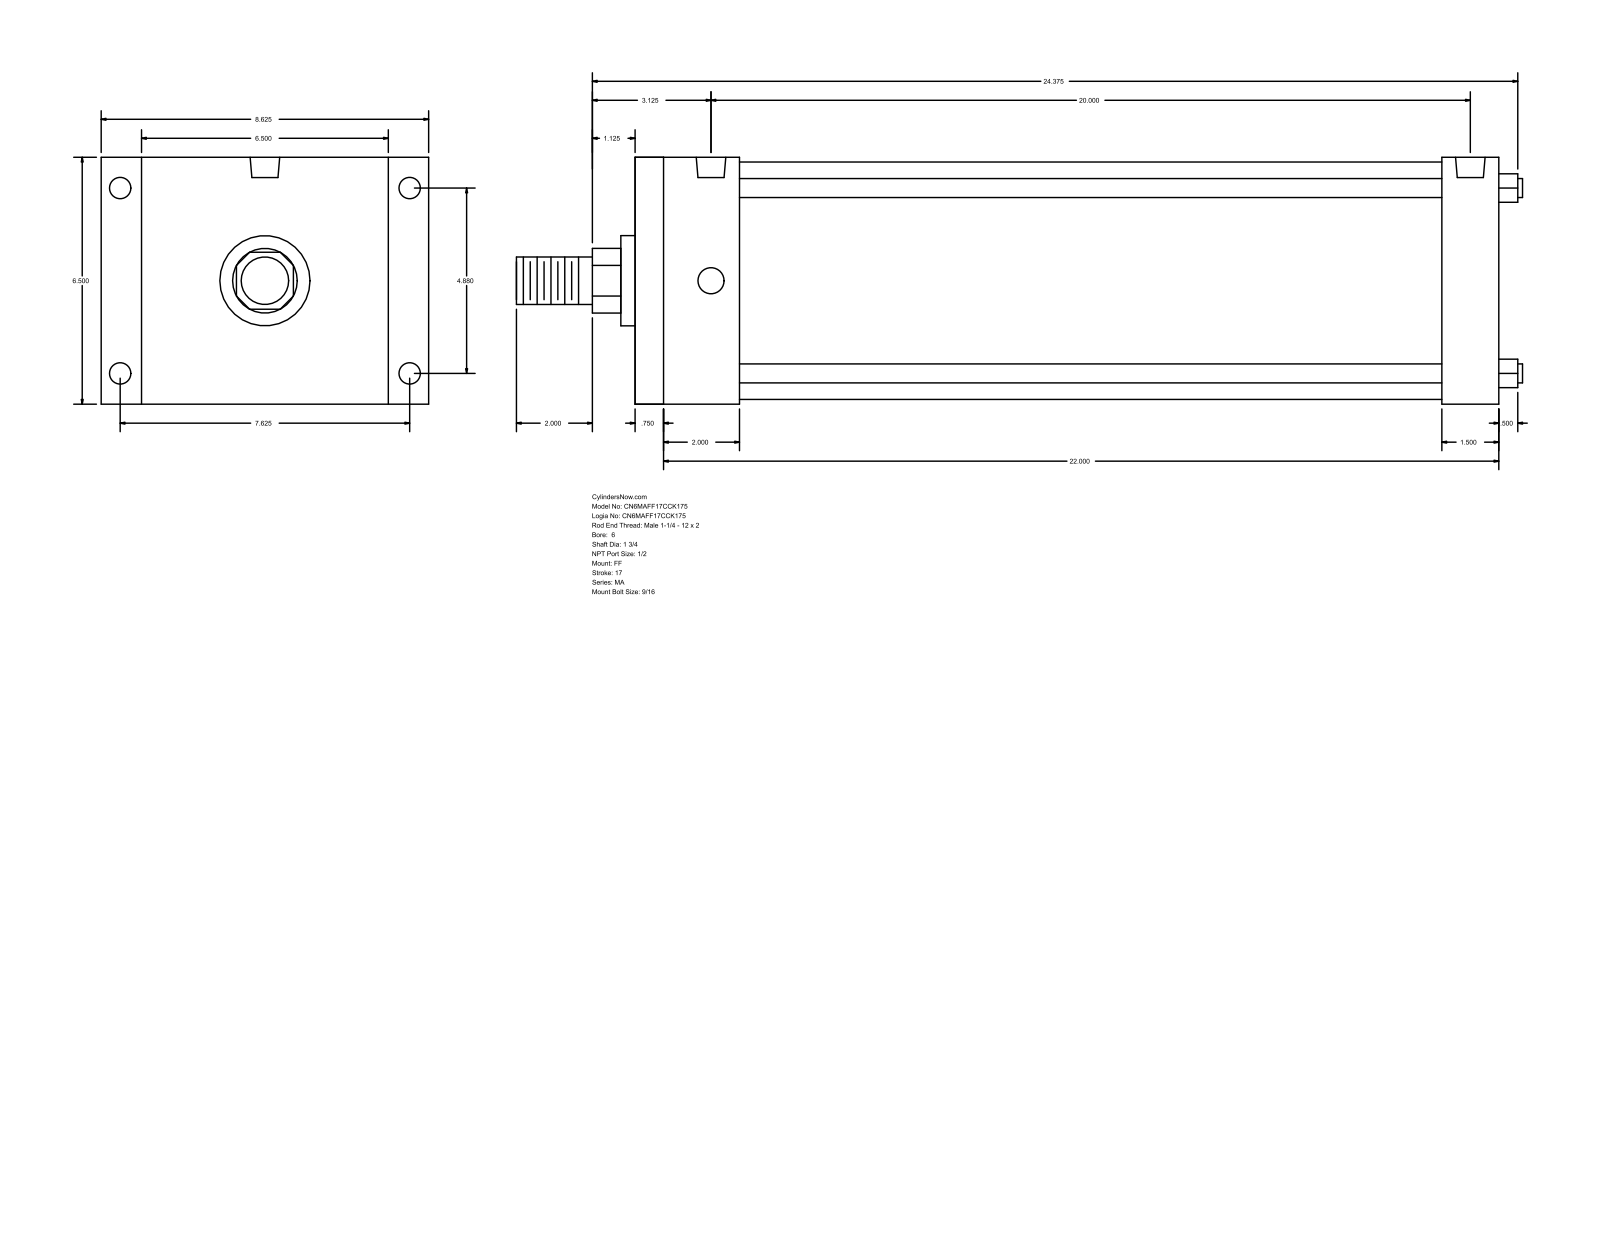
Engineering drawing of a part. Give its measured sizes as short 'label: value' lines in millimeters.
name: MA_FF__0600_1.75
written by: GSSL Pune (CONFIG_CONTROL_DESIGN)
unit: mm
bodies: 0 solids, 92 faces (64 planar, 28 cylindrical, 0 other)
size: 673.1 × 219.07 × 165.1
holes: 4× ⌀14.29, 4× ⌀17.46, 2× ⌀19.77
bosses: 4× ⌀12.7, 1× ⌀158.75, 1× ⌀60.33, 1× ⌀44.45, 1× ⌀31.75
rounds: 1× R21.63
face distances: 165.1, 577.85, 19.05, 558.8, 69.85, 50.8, 508, 539.76, 520.71, 469.91
hole spacings: 123.96, 193.68, 229.95, 508
